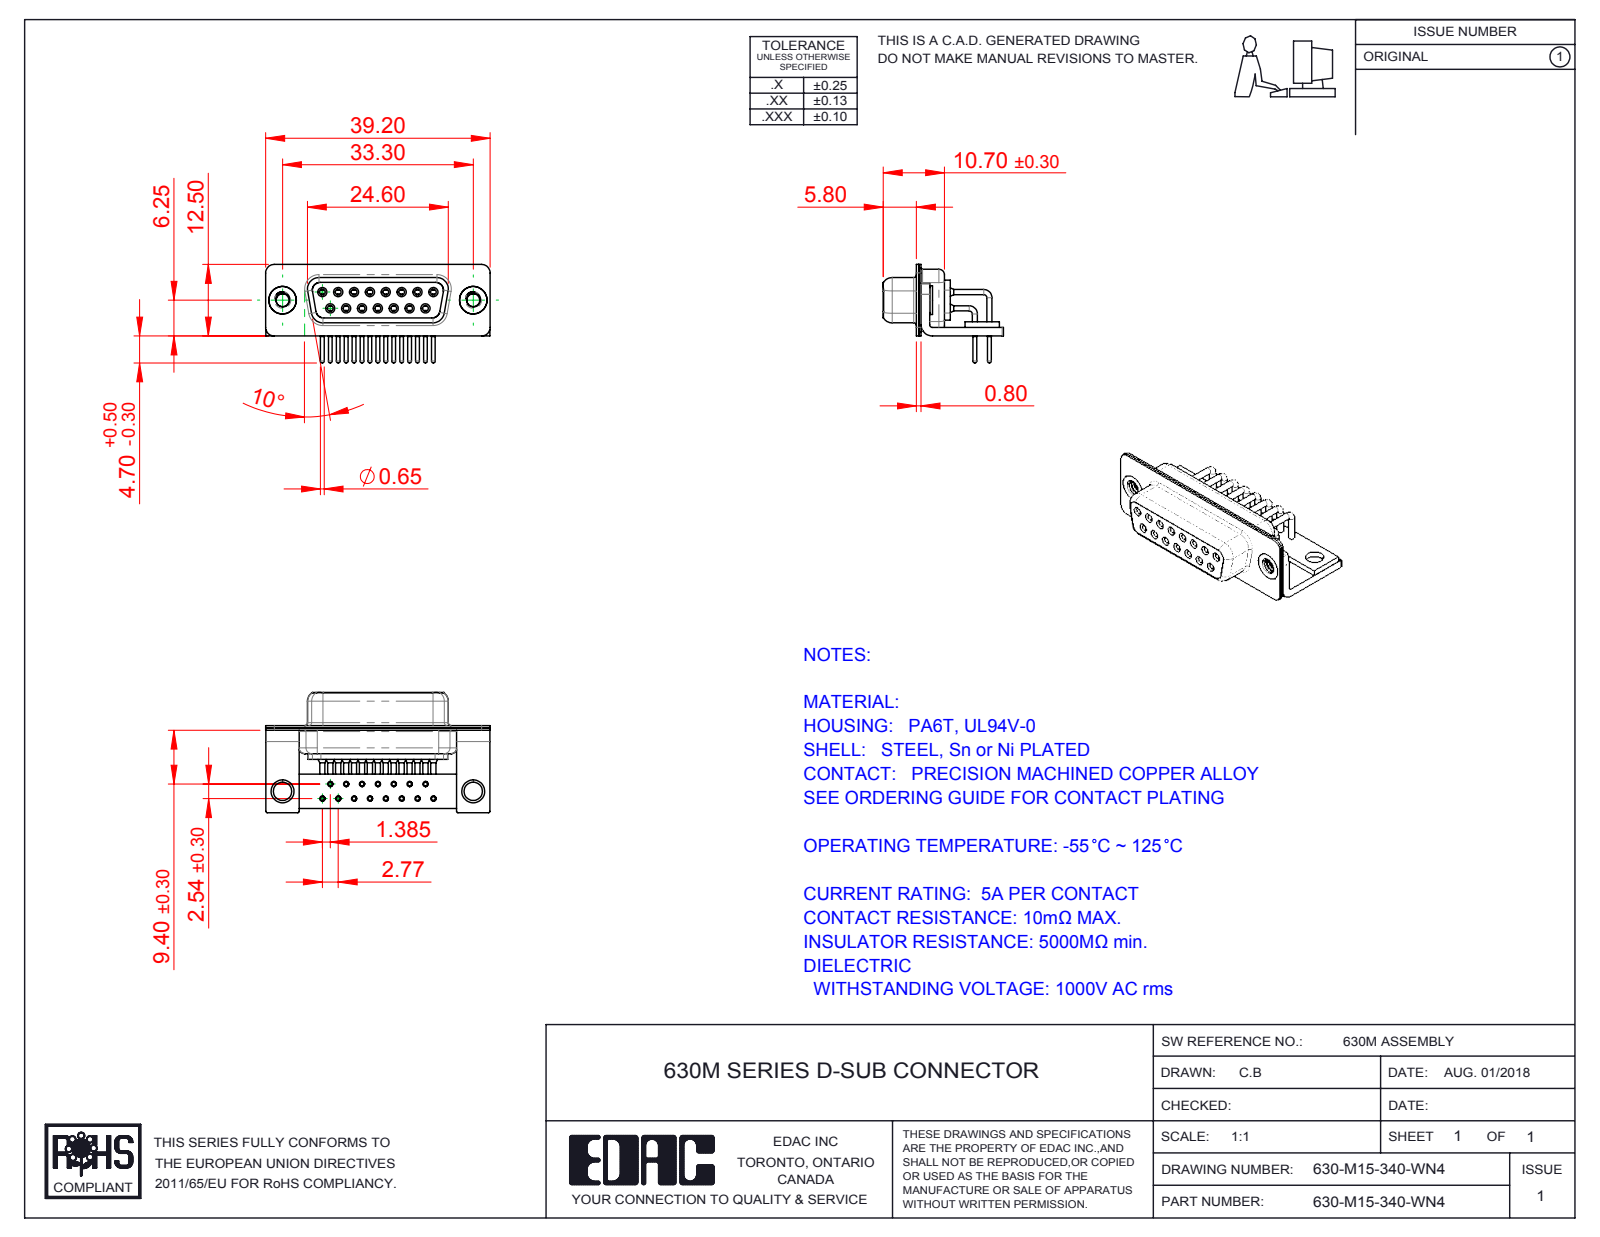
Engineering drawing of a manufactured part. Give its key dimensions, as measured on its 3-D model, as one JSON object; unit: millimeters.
{"part_name": "630M Stabilizer Board_15 Contacts; 630M Shell Front_15 Contacts; 630M Housing_15 Contacts; 630M 4-40 Threaded Rivet_Stabilizer (+5 more)", "step_written_by": "SolidWorks 2016 (CONFIG_CONTROL_DESIGN)", "units": "millimeters", "bodies": {"solids": 23, "faces": 1154, "planar": 318, "cylindrical": 534, "other": 302}, "overall_size": [39.2, 21, 17.2], "volume_mm3": 3044, "surface_area_mm2": 7715, "round_holes": [[0.9, 15], [1, 15], [1.1, 15], [1.7, 15], [1.8, 15], [2, 15], [2.26, 2], [3.2, 2], [4, 2], [4.8, 2]], "round_bosses_or_shafts": [[0.9, 27], [1.6, 15], [1.5, 15], [0.65, 15], [5, 2], [4.9, 2]], "partial_cylinders_radius": [[0.25, 16], [1.5, 16], [2, 13], [1.35, 8], [1.6, 8], [0.5, 5], [0.6, 4], [0.65, 4]], "face_to_face_distances": [0.4, 0.8, 2.3, 9.35, 1.9, 1.5, 1, 1.45, 8.95, 0.85], "hole_center_spacings": [2.77, 5.54, 8.31, 3.16, 4.87, 11.08, 2.89, 7.37]}
